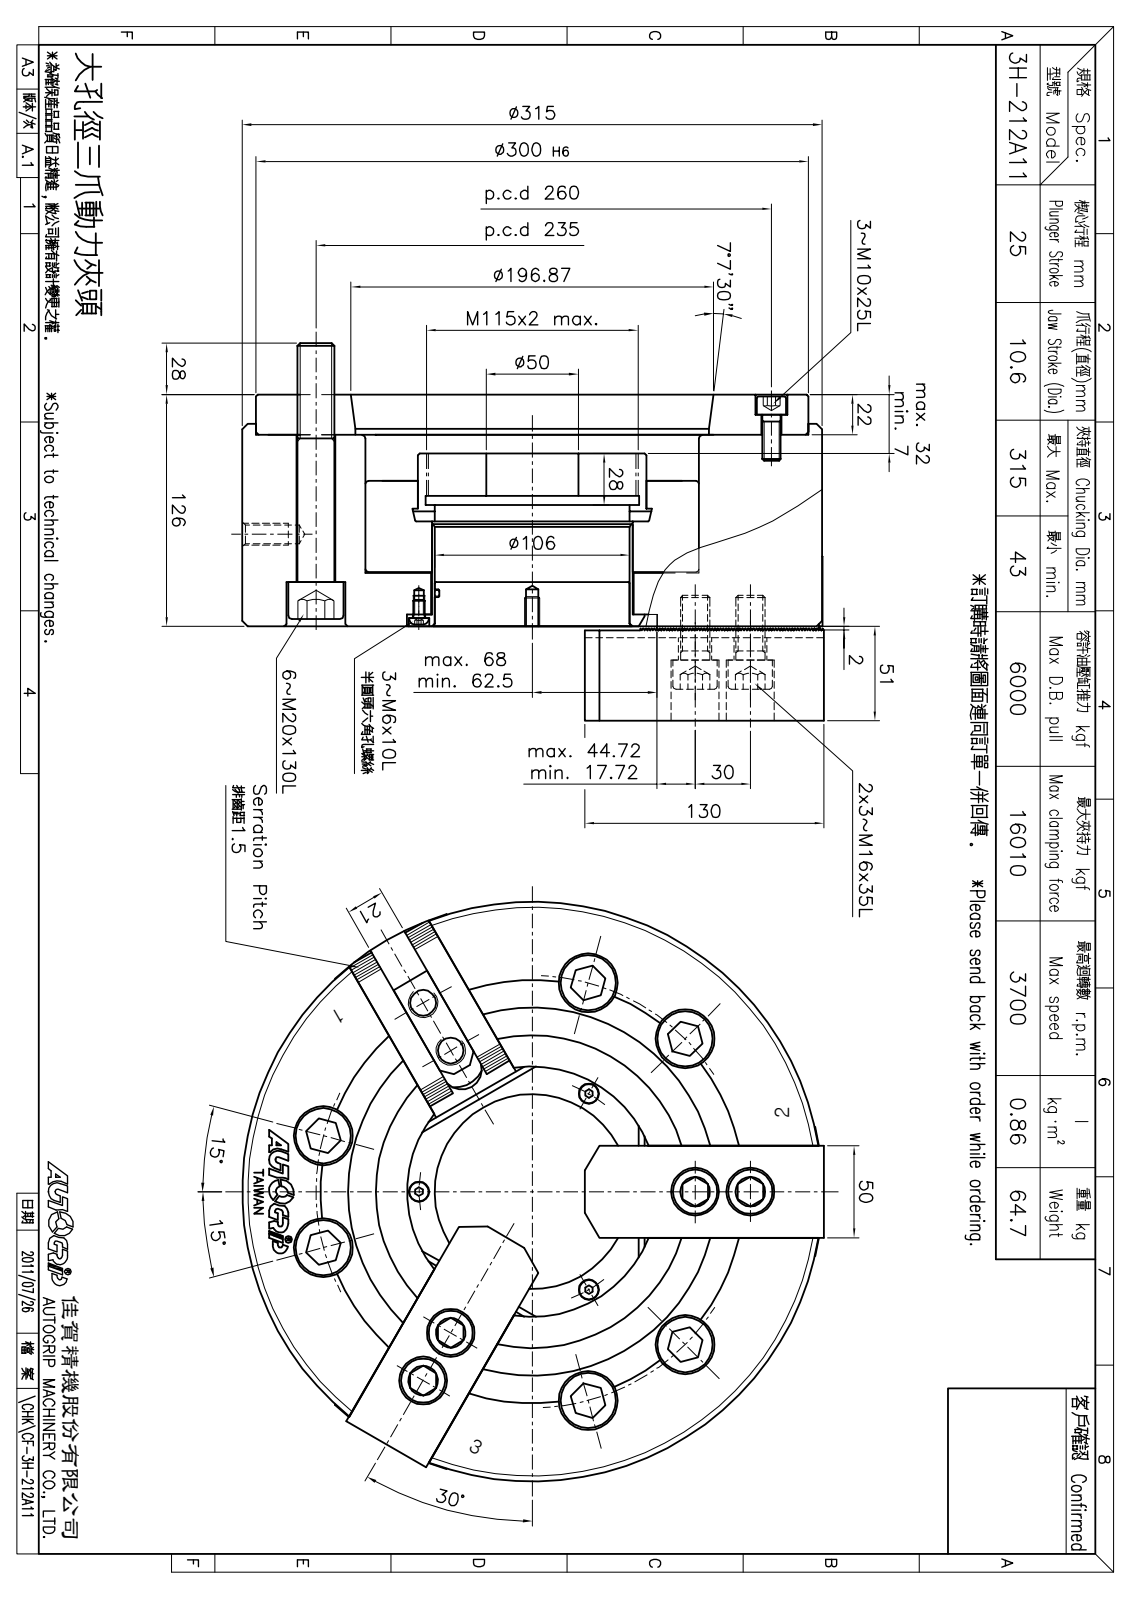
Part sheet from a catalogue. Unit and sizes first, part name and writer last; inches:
Units: inches
Overall size (bounding box): 12.443 × 12.402 × 7.293
Round holes (diameter × count): ⌀0.866 ×15, ⌀0.709 ×9, ⌀1.024 ×6, ⌀1.26 ×6, ⌀0.433 ×3, ⌀0.268 ×1, ⌀4.173 ×1, ⌀4.295 ×1, ⌀4.331 ×1, ⌀4.449 ×1, ⌀4.547 ×1, ⌀5.354 ×1
Round bosses / shafts (diameter × count): ⌀1.181 ×6, ⌀0.945 ×6, ⌀0.787 ×6, ⌀0.63 ×6, ⌀12.402 ×1, ⌀4.882 ×1, ⌀4.291 ×1, ⌀4.165 ×1
Partial cylindrical surfaces — rounded edges, fillets, slot ends (radius × count): R0.008 ×201
Main face-to-face distances: 4.094, 0.866, 4.961, 1.969, 3.819, 2.953, 1.142, 6.978, 6.112, 3.159
Hole centre spacings: 4.626, 6.542, 9.252, 2.394, 2.353, 4.663, 6.572, 8.012
Volume: 527.6 in³ · Surface area: 1 298 in²
Bodies: 20 solids, 2175 faces (1483 planar, 564 cylindrical, 128 other)
Part name (STEP PRODUCT): CF-3H-212-06000; 圓頭內六角螺栓_M16x35; SJ-12H; 圓頭內六角螺栓_M20x110 (+4 more)
STEP written by: SolidWorks 2016 (CONFIG_CONTROL_DESIGN)
